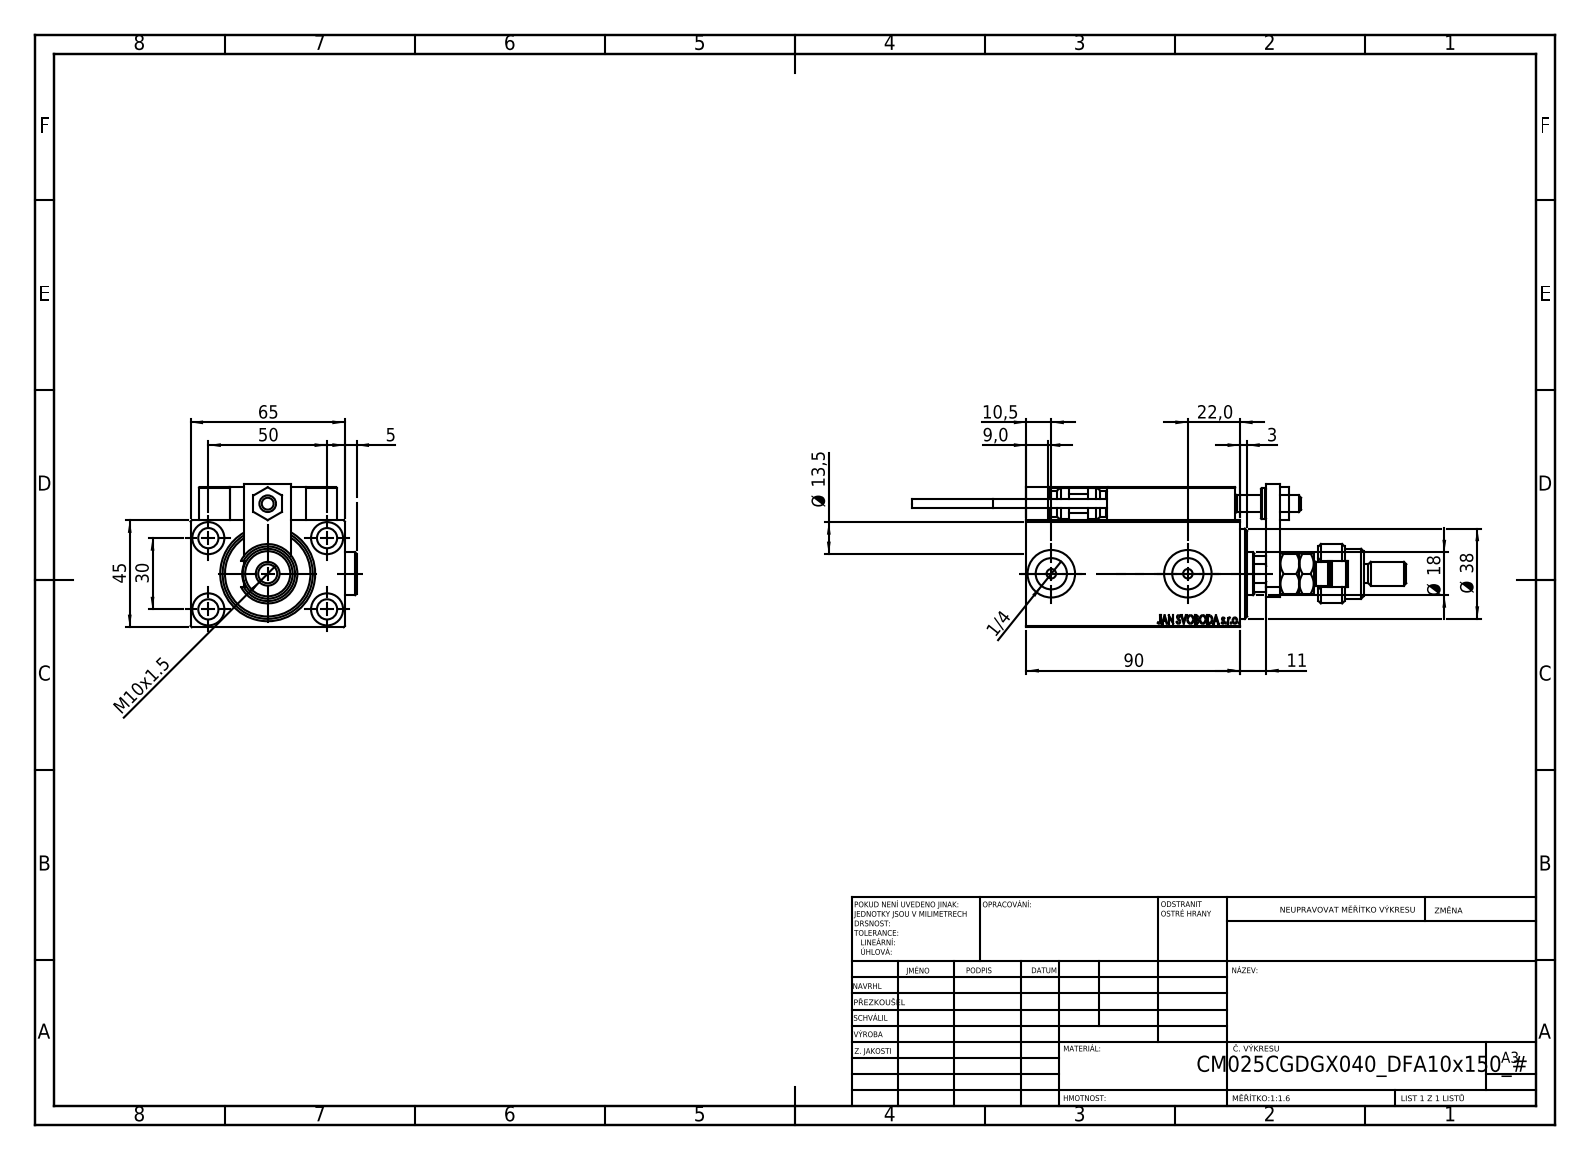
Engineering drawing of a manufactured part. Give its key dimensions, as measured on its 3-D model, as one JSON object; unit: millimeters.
{"part_name": "KONCOVKA; Block; SWITCH_X_FRONT_BACK; V450CM_VC_B (+7 more)", "step_written_by": "SolidWorks 2019 (CONFIG_CONTROL_DESIGN)", "units": "millimeters", "bodies": {"solids": 27, "faces": 1421, "planar": 622, "cylindrical": 217, "other": 582}, "overall_size": [208, 69.9, 60.5], "volume_mm3": 283658, "surface_area_mm2": 87237, "round_holes": [[4, 6], [8, 5], [8.5, 5], [3.2, 4], [13.5, 4], [5, 2], [13.16, 2], [20, 2], [7, 1], [14.5, 1], [18, 1], [21.5, 1]], "round_bosses_or_shafts": [[18, 2], [5, 2], [3.8, 2], [25, 1], [21, 1], [16, 1], [13, 1], [11, 1]], "partial_cylinders_radius": [[0.3, 30], [3, 2], [5.5, 1], [8.5, 1], [8.75, 1]], "face_to_face_distances": [45, 14, 65, 6, 59, 3, 5, 101, 13, 7], "hole_center_spacings": [29.15, 11.37, 20, 28.9, 29.59, 29.69, 30, 36.06]}
